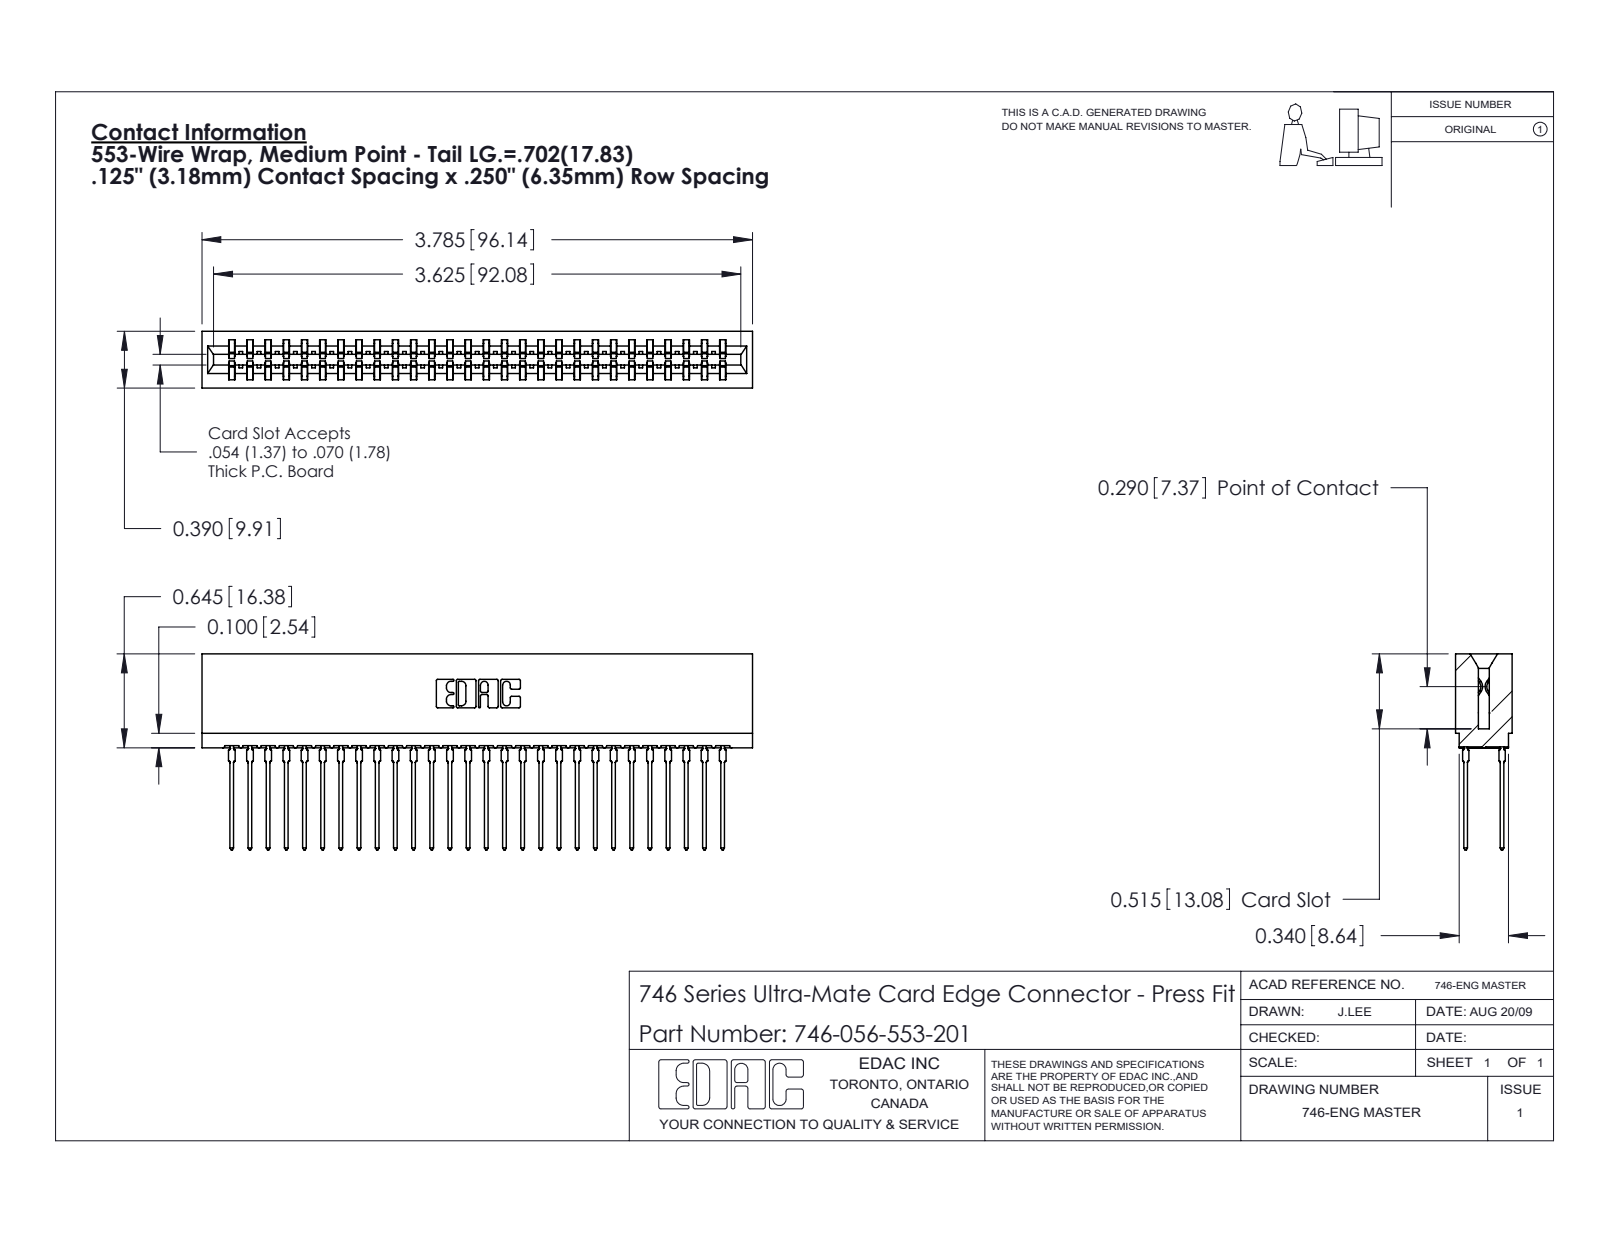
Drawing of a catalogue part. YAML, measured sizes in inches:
part_name: "746-056-553-201; 746-292-001_553; 746 Part_.515 Slot Depth - 01"
step_written_by: "SolidWorks 2020 (CONFIG_CONTROL_DESIGN)"
units: inches
bodies: {solids: 57, faces: 5109, planar: 2631, cylindrical: 1022, other: 1456}
overall_size: [3.785, 1.346, 0.39]
volume: 0.65
surface_area: 27.82
partial_cylinders:
  - {radius: 0.021, count: 112}
  - {radius: 0.015, count: 29}
  - {radius: 0.01, count: 22}
  - {radius: 0.005, count: 8}
  - {radius: 0.011, count: 8}
  - {radius: 0.007, count: 6}
  - {radius: 0.031, count: 6}
  - {radius: 0.026, count: 3}
face_to_face_distances: [0.057, 0.333, 0.25, 0.025, 0.307, 0.39, 0.083, 0.275, 0.5, 0.125]
